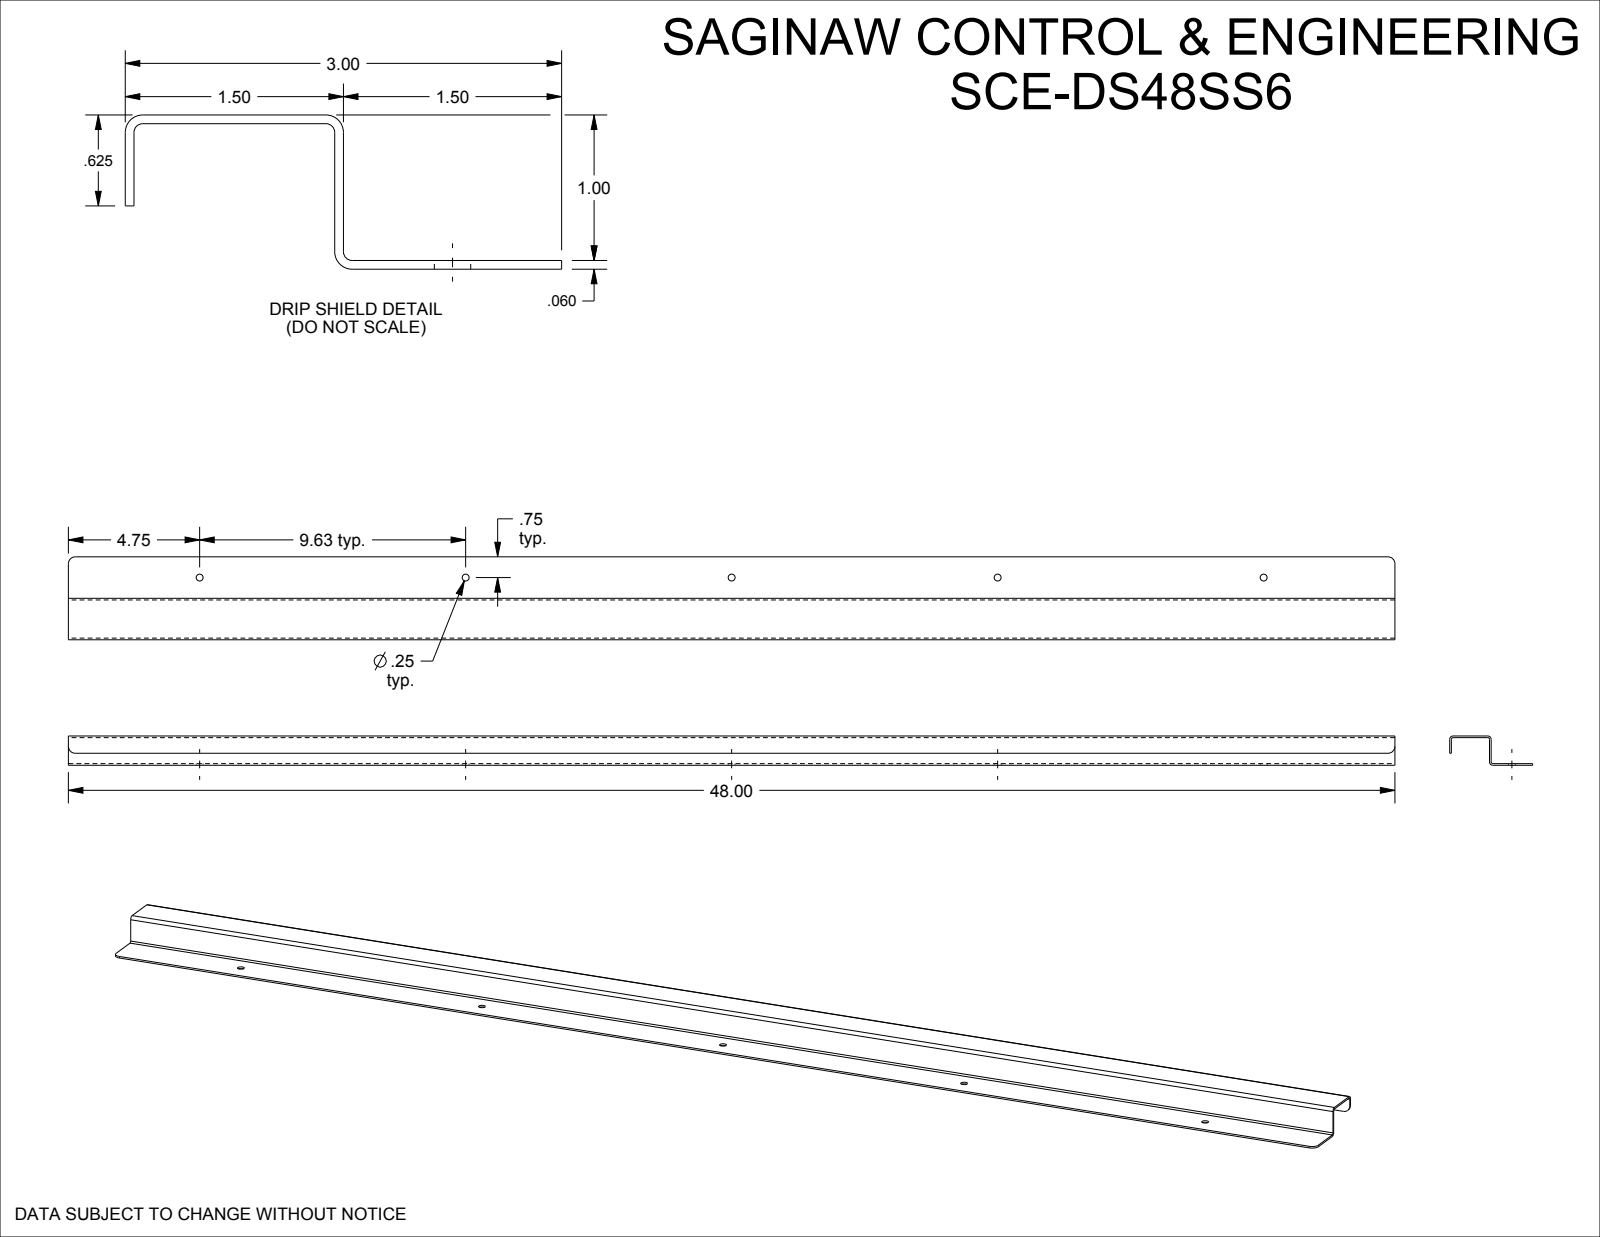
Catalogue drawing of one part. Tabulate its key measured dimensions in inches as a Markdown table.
| quantity | value |
| --- | --- |
| part name | SCE-DS48SS6 |
| STEP written by | SolidWorks 2019 (CONFIG_CONTROL_DESIGN) |
| units | inches |
| bodies | 1 solid, 27 faces (12 planar, 15 cylindrical, 0 other) |
| overall size | 48 × 3 × 1.06 |
| volume | 12.8 in³ |
| surface area | 433 in² |
| round holes (diameter × count) | 0.25 × 5 |
| partial cylindrical surfaces (radius × count) | 0.25 × 4, 0.06 × 3, 0.12 × 3 |
| main face-to-face distances | 0.06, 1, 1.06, 0.94, 1.44, 1.5, 1.38, 0.435, 0.375, 0.565 |
| hole center spacings | 9.625, 9.625, 19.25, 28.875, 19.25, 38.5 |
